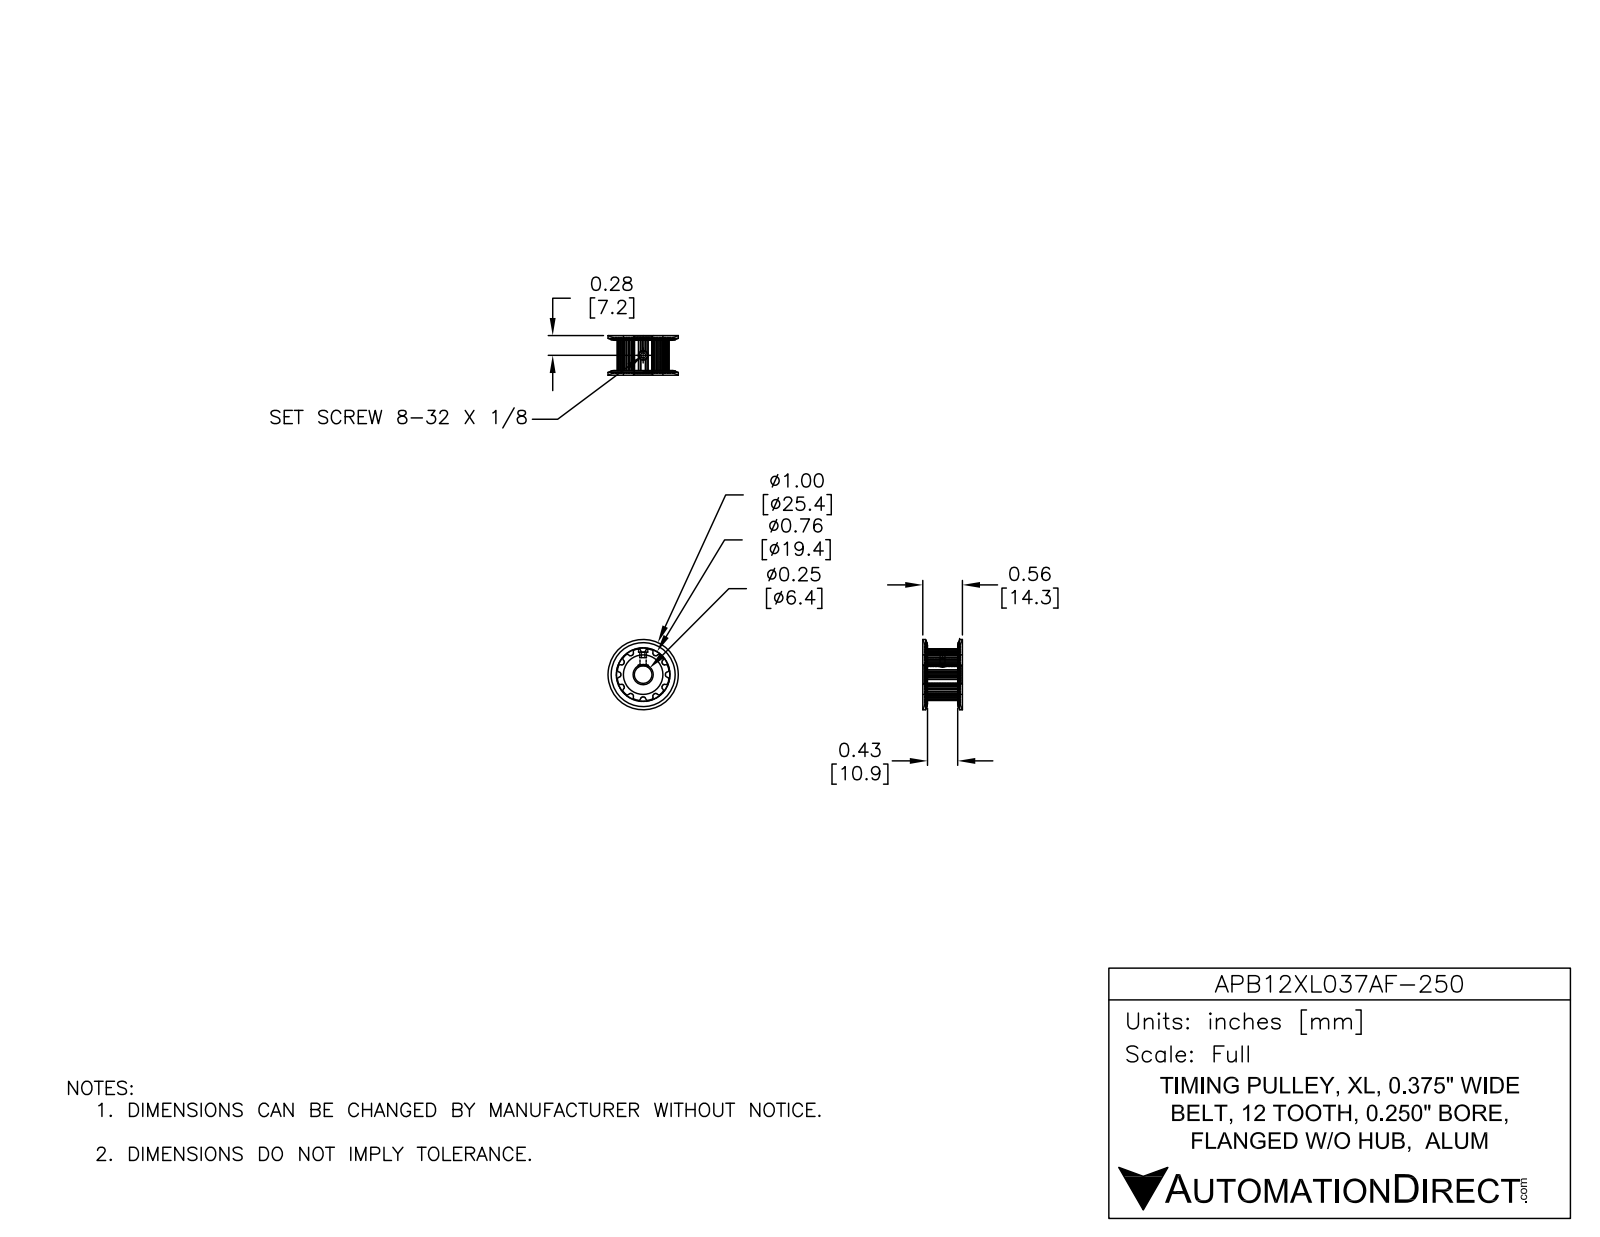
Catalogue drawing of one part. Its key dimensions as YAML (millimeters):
part_name: "APB12XL037AF-250"
step_written_by: "SolidWorks 2014 (AUTOMOTIVE_DESIGN)"
units: millimeters
bodies: {solids: 1, faces: 155, planar: 48, cylindrical: 87, other: 20}
overall_size: [25.4, 25.4, 14.3]
volume: 3240
surface_area: 2844
round_holes:
  - {diameter: 2.2, count: 2}
  - {diameter: 6.4, count: 1}
round_bosses_or_shafts:
  - {diameter: 12.6, count: 1}
partial_cylinders:
  - {radius: 0.4, count: 43}
  - {radius: 0.2, count: 4}
  - {radius: 1.6, count: 2}
  - {radius: 8.1, count: 1}
face_to_face_distances: [0.8, 12.7, 13.5, 18.9, 1.6, 11.9, 14.3, 5.6, 11.1, 5.6]
